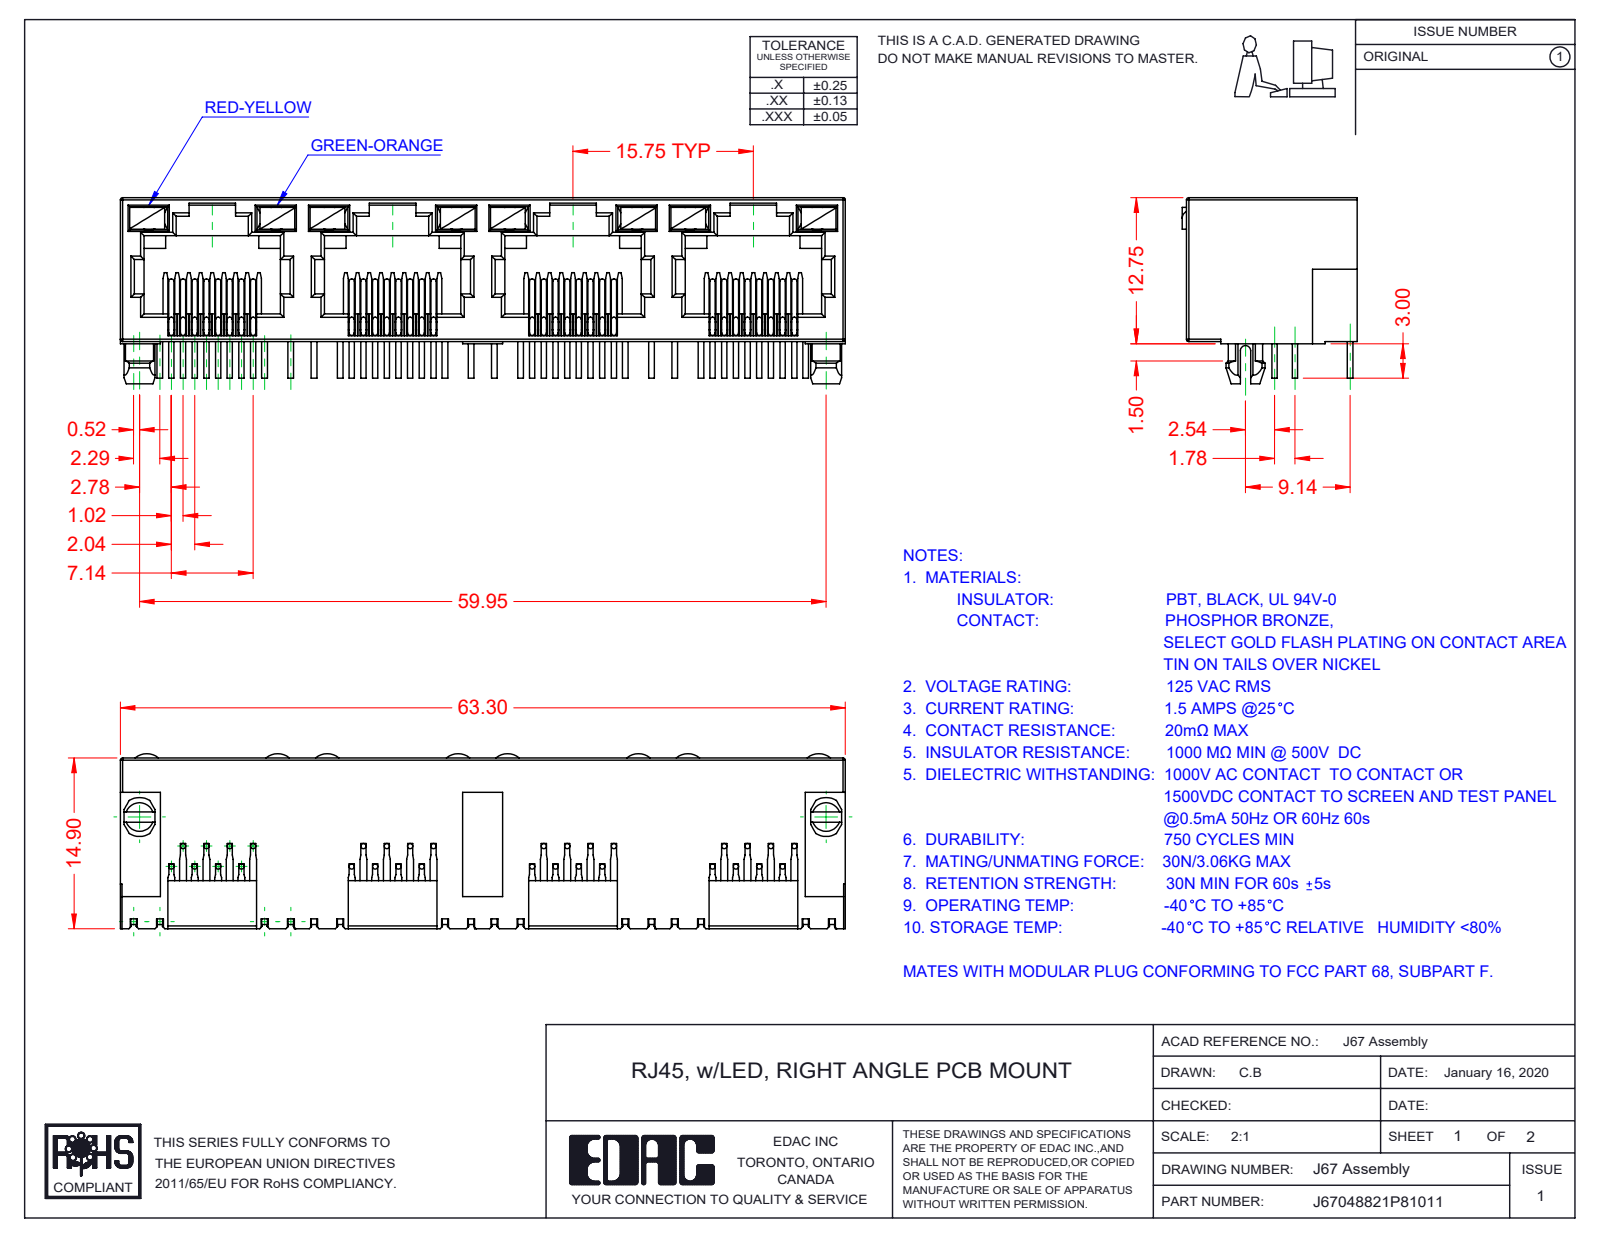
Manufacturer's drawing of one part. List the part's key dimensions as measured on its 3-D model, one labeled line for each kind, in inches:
Part name (STEP PRODUCT): 67 LED LH_8-Red-Yellow; 67 Insulator; 67 Contacts; 67 LED RH_7-Green-Orange (+1 more)
STEP written by: SolidWorks 2016 (CONFIG_CONTROL_DESIGN)
Units: inches
Bodies: 41 solids, 2481 faces (1781 planar, 492 cylindrical, 208 other)
Overall size (bounding box): 2.492 × 0.64 × 0.602
Volume: 0.315 in³ · Surface area: 17.94 in²
Round bosses / shafts (diameter × count): ⌀0.018 ×96
Partial cylindrical surfaces — rounded edges, fillets, slot ends (radius × count): R0.008 ×66, R0.012 ×29, R0.018 ×9, R0.061 ×8, R0.059 ×2, R0.067 ×2, R0.014 ×1, R0.039 ×1
Main face-to-face distances: 0.02, 0.494, 0.074, 0.035, 0.394, 0.62, 0.039, 0.055, 0.433, 0.468
